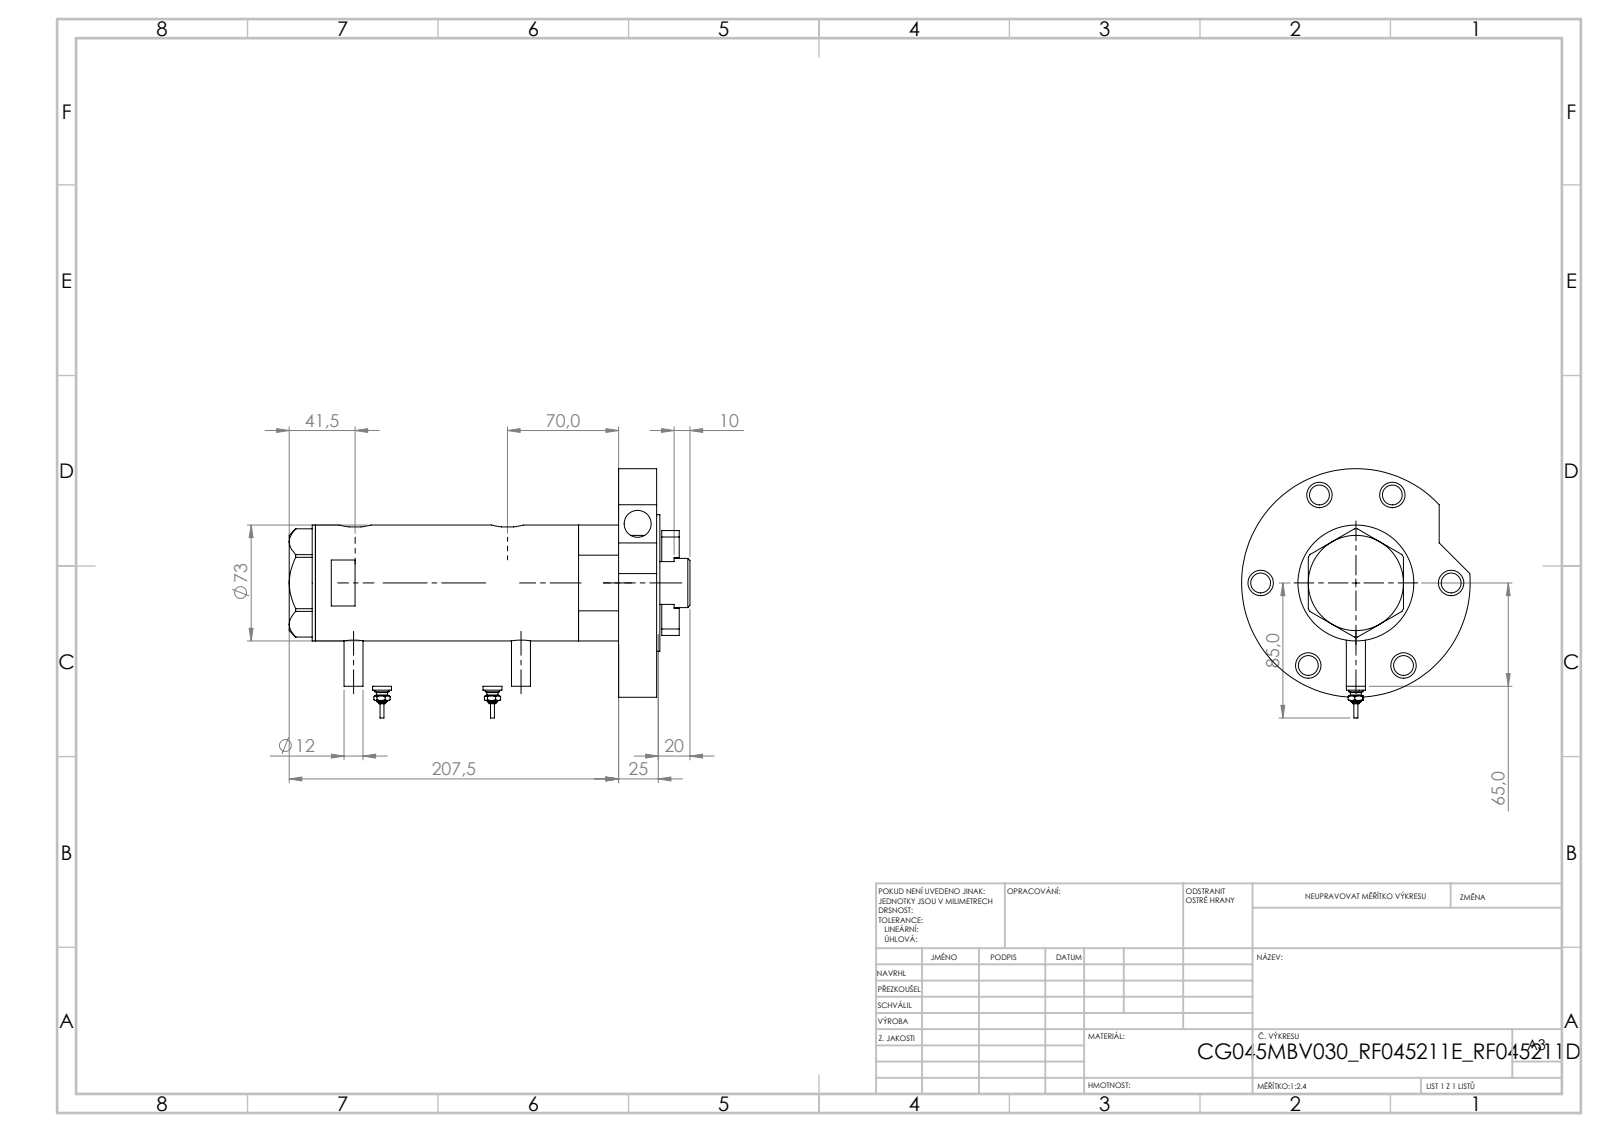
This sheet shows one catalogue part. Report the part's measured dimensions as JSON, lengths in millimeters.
{"part_name": "V270CG_RF211D; V270CG_FRONT; V270CG_RF211E; Switch (+3 more)", "step_written_by": "SolidWorks 2019 (CONFIG_CONTROL_DESIGN)", "units": "millimeters", "bodies": {"solids": 9, "faces": 296, "planar": 112, "cylindrical": 120, "other": 64}, "overall_size": [252.5, 157, 144], "volume_mm3": 1189000, "surface_area_mm2": 210904, "round_holes": [[12.5, 8], [16, 6], [8.1, 4], [13.5, 4], [13.16, 2], [10.5, 1], [17, 1], [32, 1], [33.5, 1], [45, 1], [48, 1], [60, 1]], "round_bosses_or_shafts": [[12, 4], [9, 2], [7, 2], [4.5, 2], [2.5, 2], [144, 1], [86, 1], [73, 1]], "partial_cylinders_radius": [[10, 2]], "face_to_face_distances": [24, 191, 26, 95, 2, 215, 217, 1, 121, 70], "hole_center_spacings": [60, 25.14, 57.72, 71.64, 15, 35.04, 35.9, 43.78]}
